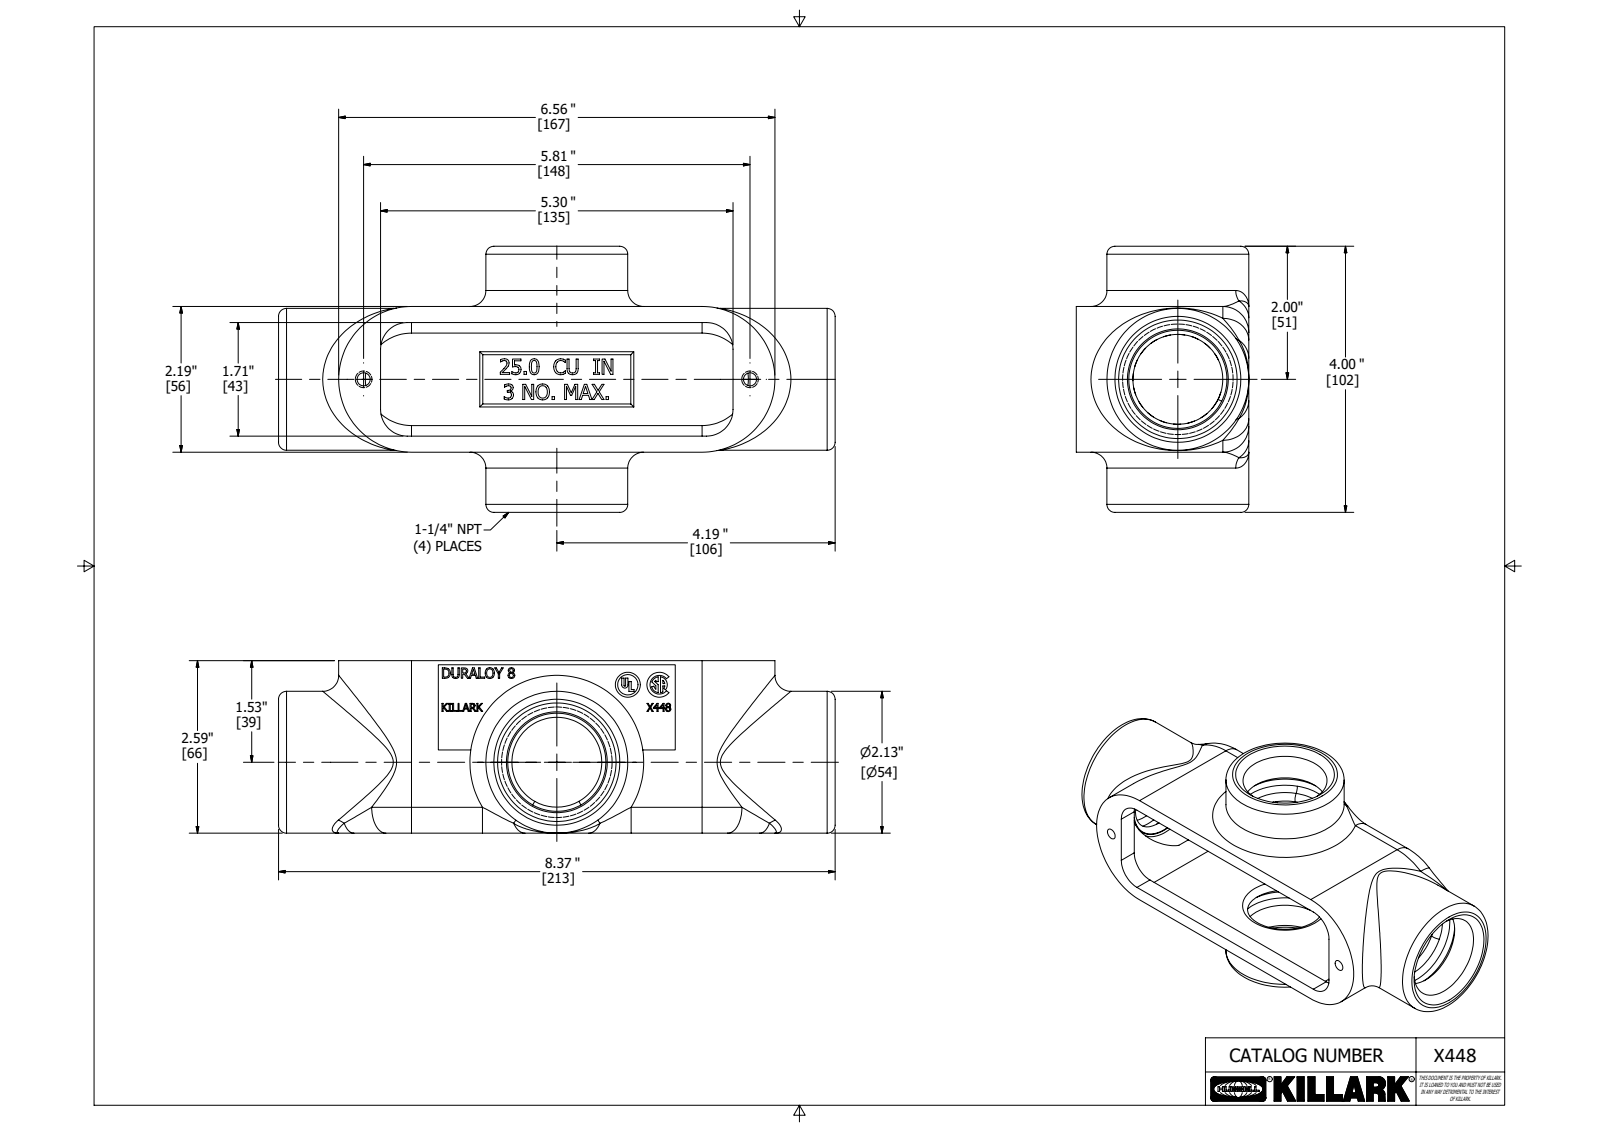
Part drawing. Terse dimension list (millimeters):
name: 21757-2
written by: Autodesk Inventor 2018 (AUTOMOTIVE_DESIGN)
unit: mm
bodies: 1 solid, 667 faces (387 planar, 41 cylindrical, 239 other)
size: 212.6 × 101.6 × 65.9
volume: 256 100 mm³; area: 88 450 mm²
holes: 2× ⌀5, 2× ⌀42.3, 1× ⌀7.8, 1× ⌀41
bosses: 2× ⌀54.2, 1× ⌀9.5
rounds: 4× R10.2, 2× R5.1, 2× R9.9, 2× R22.7, 2× R27.8, 1× R0.3, 1× R1.2, 1× R2.2
face distances: 5.1, 50.5, 45.5, 65.9, 60.8, 1, 6.1, 49.5, 44.4, 55.6
hole spacings: 40.1, 147.6
